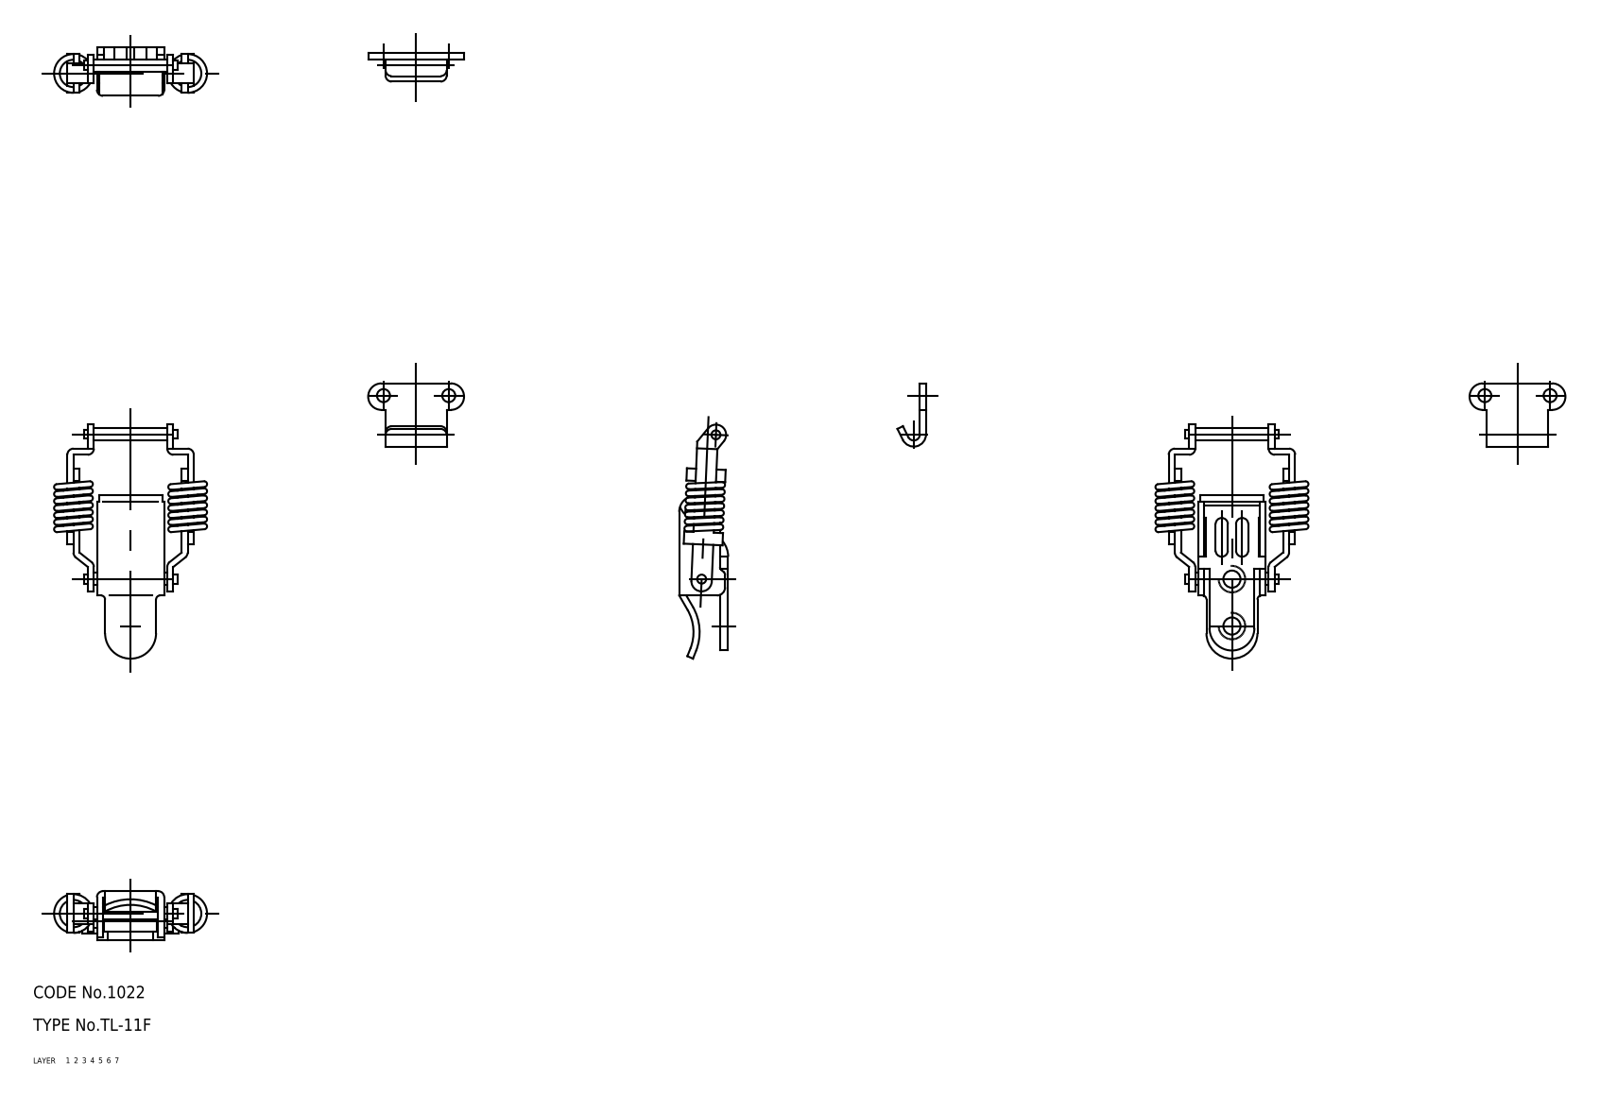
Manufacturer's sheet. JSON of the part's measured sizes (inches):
{"part_name": "arm_B_mr; spring; arm_A_mr; shaft_B (+7 more)", "step_written_by": "CADfix (AUTOMOTIVE_DESIGN)", "units": "inches", "bodies": {"solids": 11, "faces": 273, "planar": 0, "cylindrical": 0, "other": 273}, "overall_size": [2.657, 1.476, 0.472], "volume_in3": 0.288, "surface_area_in2": 12.85}
